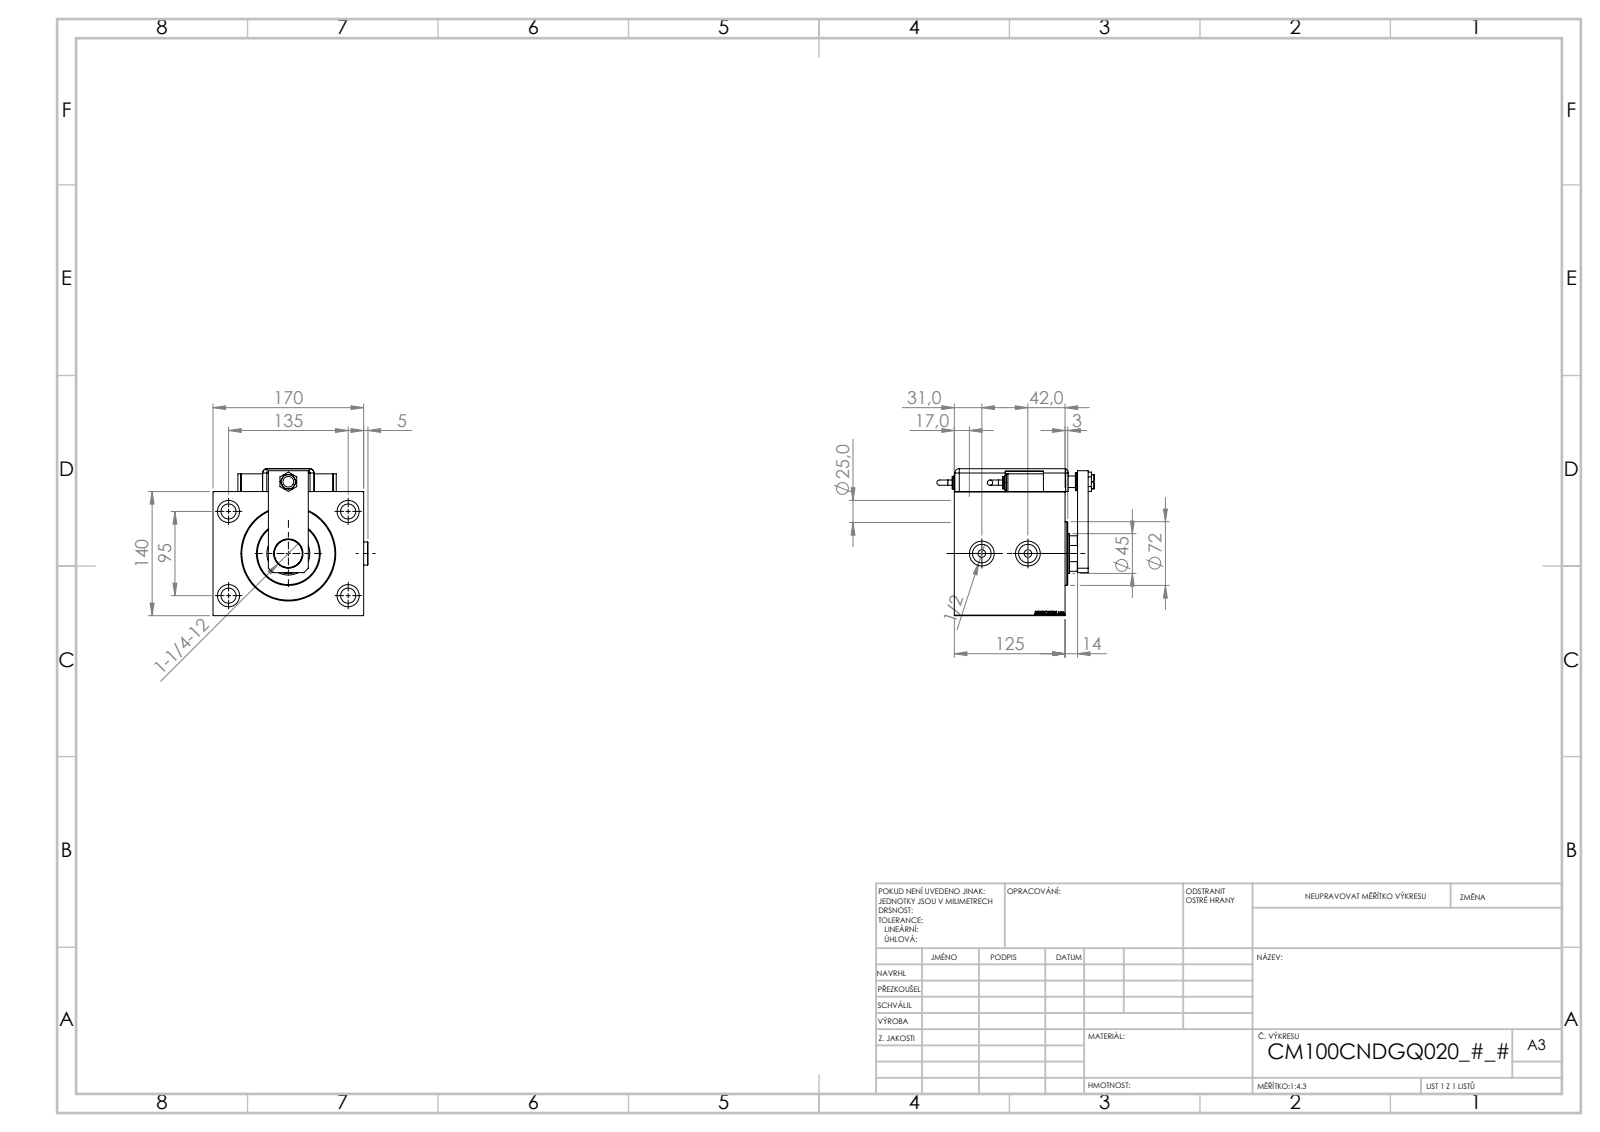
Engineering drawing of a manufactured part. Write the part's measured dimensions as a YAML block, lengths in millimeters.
part_name: "MAGNETIC SWITCH Q; ZARAZKA_Q; SWITCH DIM A_G; NUT_D19 (+7 more)"
step_written_by: "SolidWorks 2019 (CONFIG_CONTROL_DESIGN)"
units: millimeters
bodies: {solids: 13, faces: 1263, planar: 619, cylindrical: 127, other: 517}
overall_size: [177.66, 170, 165.8]
volume: 2857000
surface_area: 304570
round_holes:
  - {diameter: 17, count: 4}
  - {diameter: 25, count: 4}
  - {diameter: 4, count: 2}
  - {diameter: 8, count: 2}
  - {diameter: 8.5, count: 2}
  - {diameter: 20.96, count: 2}
  - {diameter: 28, count: 2}
  - {diameter: 12, count: 1}
  - {diameter: 13, count: 1}
  - {diameter: 14, count: 1}
  - {diameter: 31.5, count: 1}
  - {diameter: 33, count: 1}
round_bosses_or_shafts:
  - {diameter: 20, count: 3}
  - {diameter: 16, count: 2}
  - {diameter: 14, count: 2}
  - {diameter: 6, count: 2}
  - {diameter: 72, count: 1}
partial_cylinders:
  - {radius: 5, count: 9}
  - {radius: 10, count: 1}
  - {radius: 22, count: 1}
face_to_face_distances: [140, 125, 170, 61.25, 63.75, 3, 20, 10, 25, 115]
hole_center_spacings: [82.54, 75.36, 95, 135, 145.15, 165.08, 20, 52]
